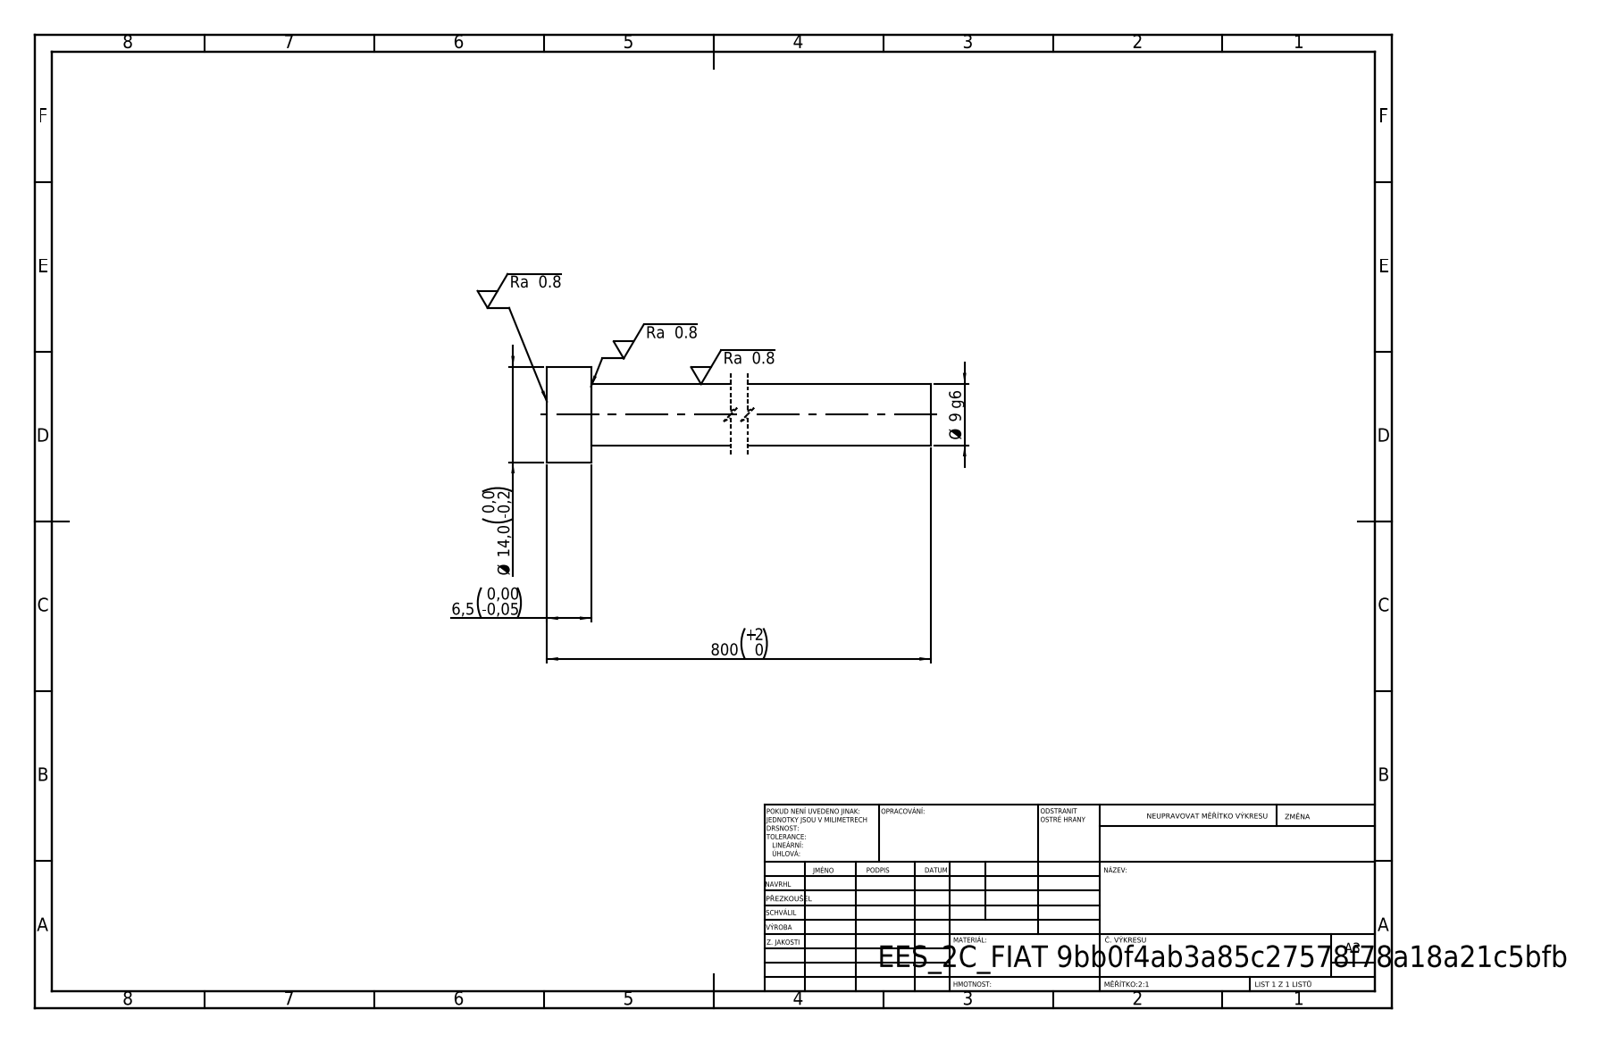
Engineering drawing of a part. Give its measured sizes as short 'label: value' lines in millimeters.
written by: SolidWorks 2019 (CONFIG_CONTROL_DESIGN)
unit: mm
bodies: 1 solid, 7 faces (3 planar, 4 cylindrical, 0 other)
size: 800 × 14 × 14
volume: 51 481 mm³; area: 23 029 mm²
bosses: 1× ⌀14, 1× ⌀9
face distances: 6.5, 800, 793.5
